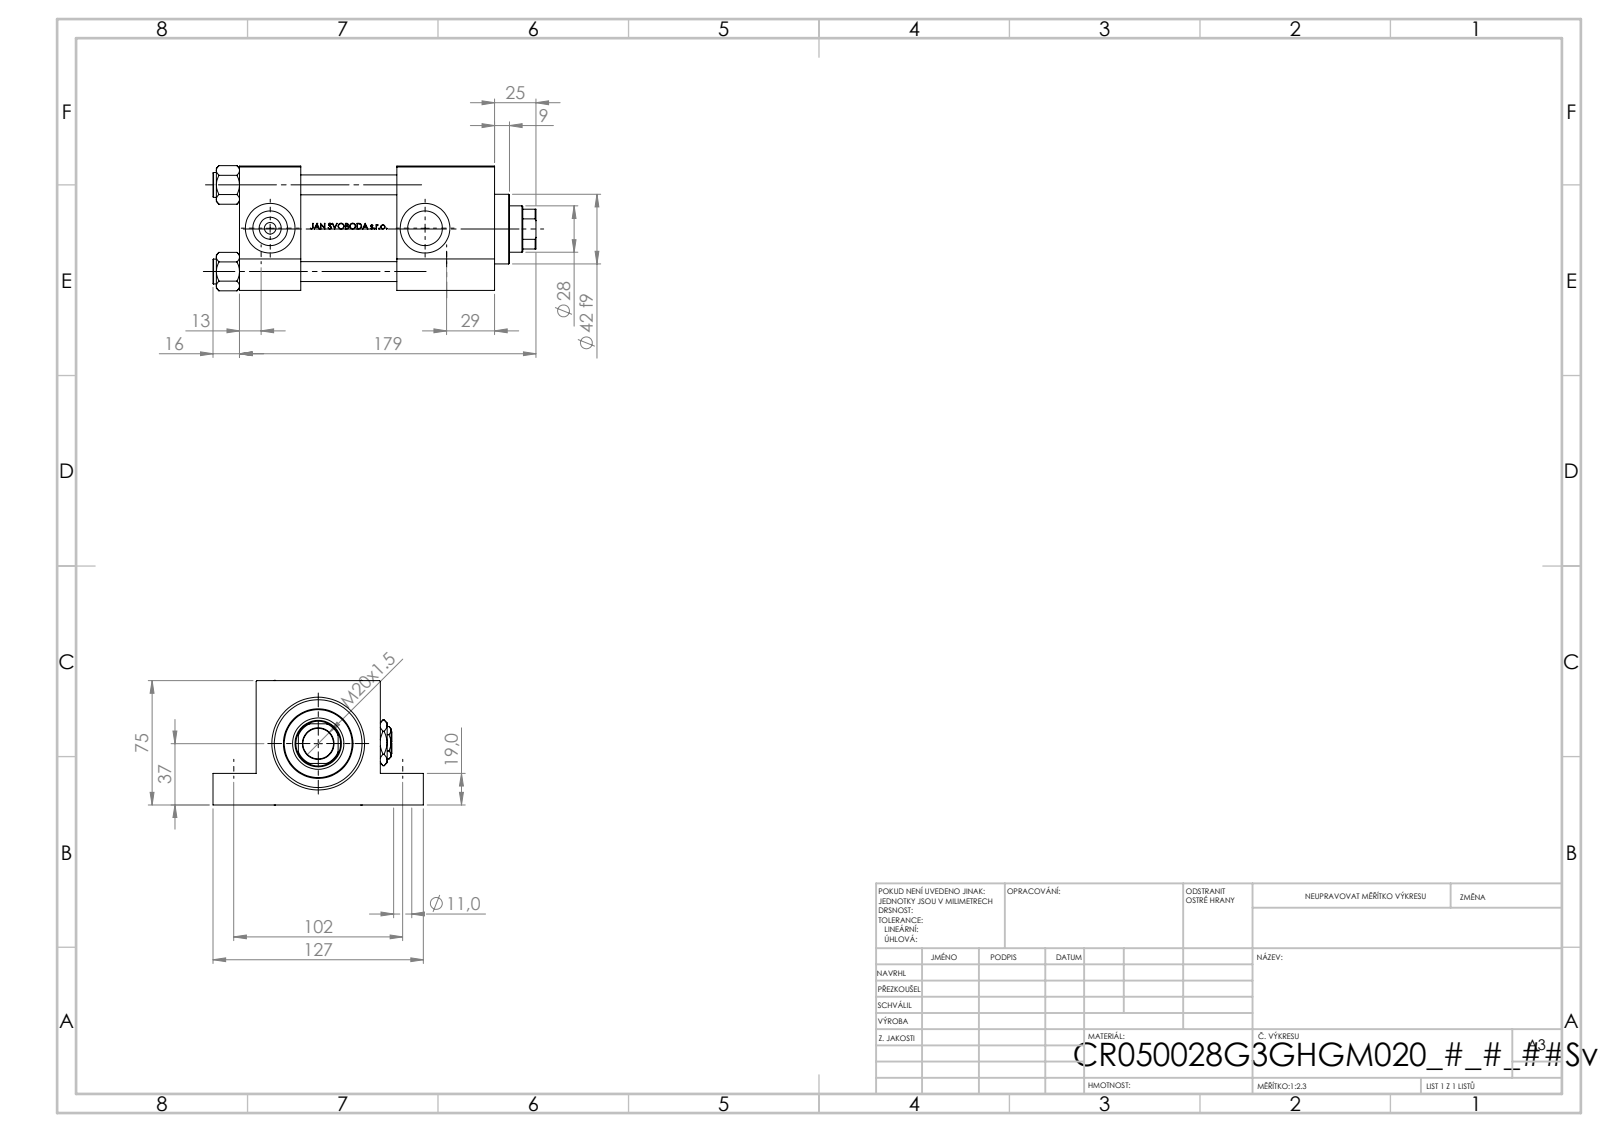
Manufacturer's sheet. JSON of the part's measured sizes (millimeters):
{"part_name": "V215_VC_A; V215CR_VCP_G; V215CR_G_Body; NUT_M5_G (+2 more)", "step_written_by": "SolidWorks 2019 (CONFIG_CONTROL_DESIGN)", "units": "millimeters", "bodies": {"solids": 13, "faces": 1183, "planar": 477, "cylindrical": 132, "other": 574}, "overall_size": [195, 127, 75.54], "volume_mm3": 762343, "surface_area_mm2": 167563, "round_holes": [[12, 4], [11, 3], [7, 2], [20.96, 2], [30, 2], [11, 1], [18.5, 1], [28, 1], [31, 1], [41, 1], [50, 1], [53, 1]], "round_bosses_or_shafts": [[15, 4], [56, 1], [42, 1]], "partial_cylinders_radius": [[13.5, 1]], "face_to_face_distances": [75, 37, 154, 117, 19, 56, 95, 58, 59, 26], "hole_center_spacings": [52.3, 36.63, 37.34, 73.96, 102, 112, 151.49, 93.5]}
